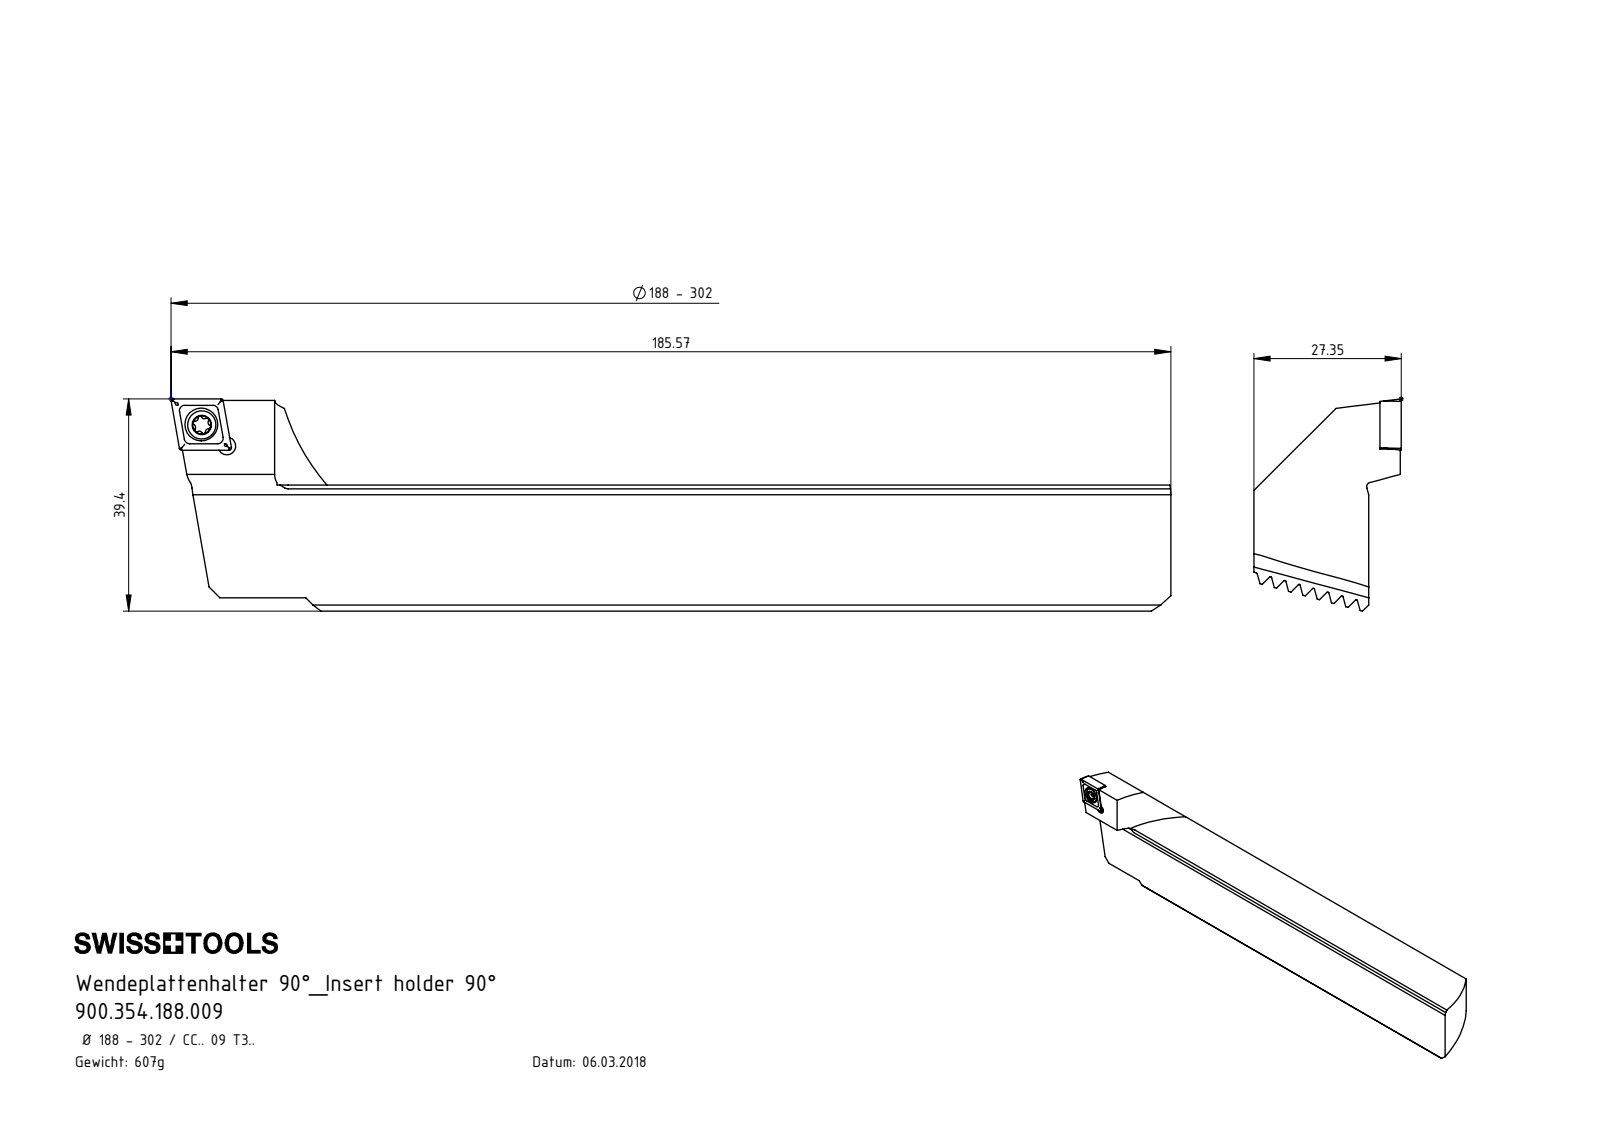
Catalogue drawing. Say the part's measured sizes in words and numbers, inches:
The part is named "900.354.188.009; CCMT09T304; WCB-ER2.001.009_A; F00-WCB.188.001_C". Its 3-D file was written by "SolidWorks 2017 (CONFIG_CONTROL_DESIGN)". It is 3 solids with 694 faces: 422 planar, 39 cylindrical and 233 other. Overall it measures 7.306 by 1.551 by 1.077 inches. Its volume is 4.719 cubic inches and its surface area 29.34 square inches. Round holes: 2 of diameter 0.13, 1 of diameter 0.173, 1 of diameter 0.24. Round bosses or shafts: 1 of diameter 0.207, 1 of diameter 0.157. Partial cylindrical surfaces (rounded edges, fillets, slot ends): 8 of radius 0.008, 6 of radius 0.013, 6 of radius 0.023, 3 of radius 1.575, 1 of radius 0.031. The main face-to-face distances are 0.094, 0.839, 0.187, 0.281, 0.375, 0.188, 0.281, 0.375, 0.469, 0.563. The hole center spacings are 0.239, 0.244.
